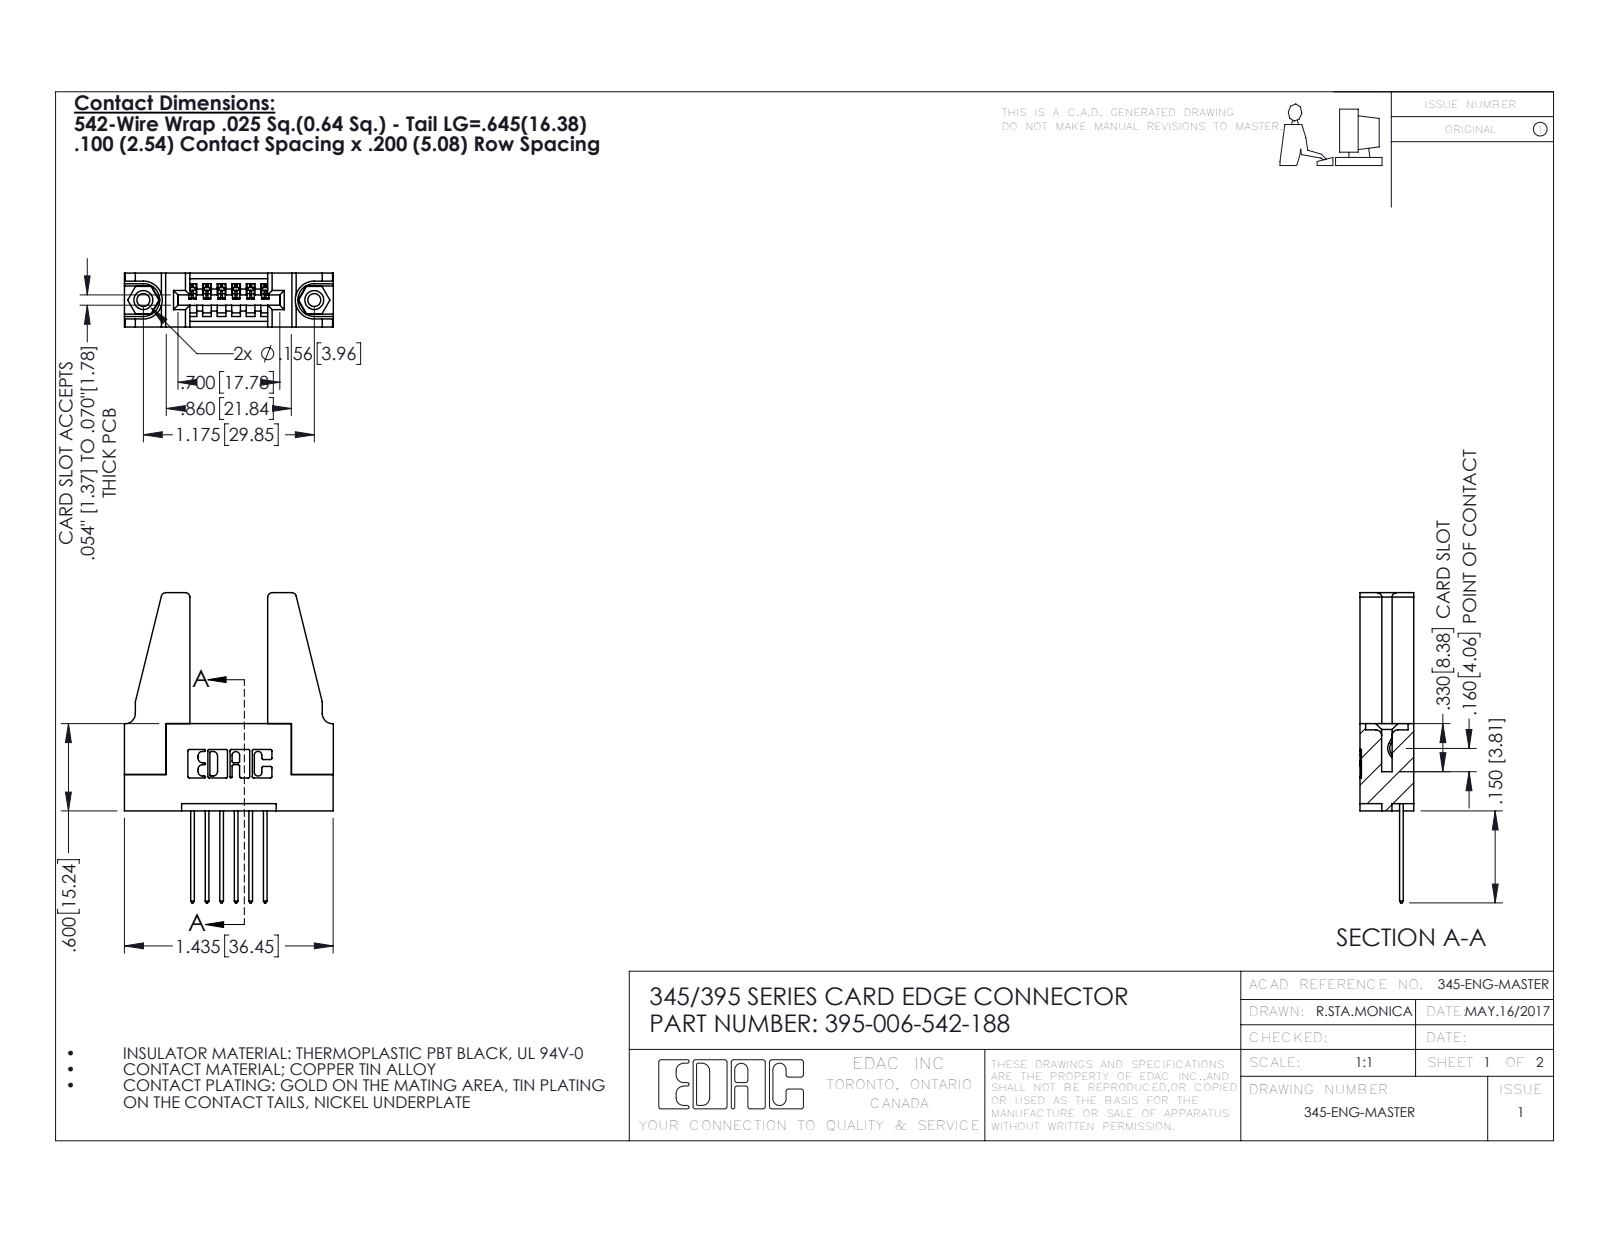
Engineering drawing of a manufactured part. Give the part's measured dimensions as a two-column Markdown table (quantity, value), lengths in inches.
| quantity | value |
| --- | --- |
| part name | 345 Part_Flush Mounting Lugs - 0.156 Dia-TH; 395-006-542-188; 345-292-001_345-293-142; 345-220-078_345-220-088 (+1 more) |
| STEP written by | SolidWorks 2016 (CONFIG_CONTROL_DESIGN) |
| units | inches |
| bodies | 11 solids, 598 faces (392 planar, 190 cylindrical, 16 other) |
| overall size | 2.132 × 1.436 × 0.37 |
| volume | 0.393 in³ |
| surface area | 10.78 in² |
| round holes (diameter × count) | 0.089 × 2, 0.125 × 2, 0.156 × 2, 0.064 × 1 |
| round bosses / shafts (diameter × count) | 0.155 × 2 |
| partial cylindrical surfaces (radius × count) | 0.01 × 22, 0.006 × 12, 0.01 × 12, 0.03 × 8, 0.007 × 6, 0.031 × 6, 0.026 × 3, 0.031 × 2 |
| main face-to-face distances | 0.37, 0.072, 0.2, 0.298, 0.098, 0.272, 0.025, 0.698, 0.15, 0.148 |
| hole center spacings | 0.27, 0.946, 1.175 |
